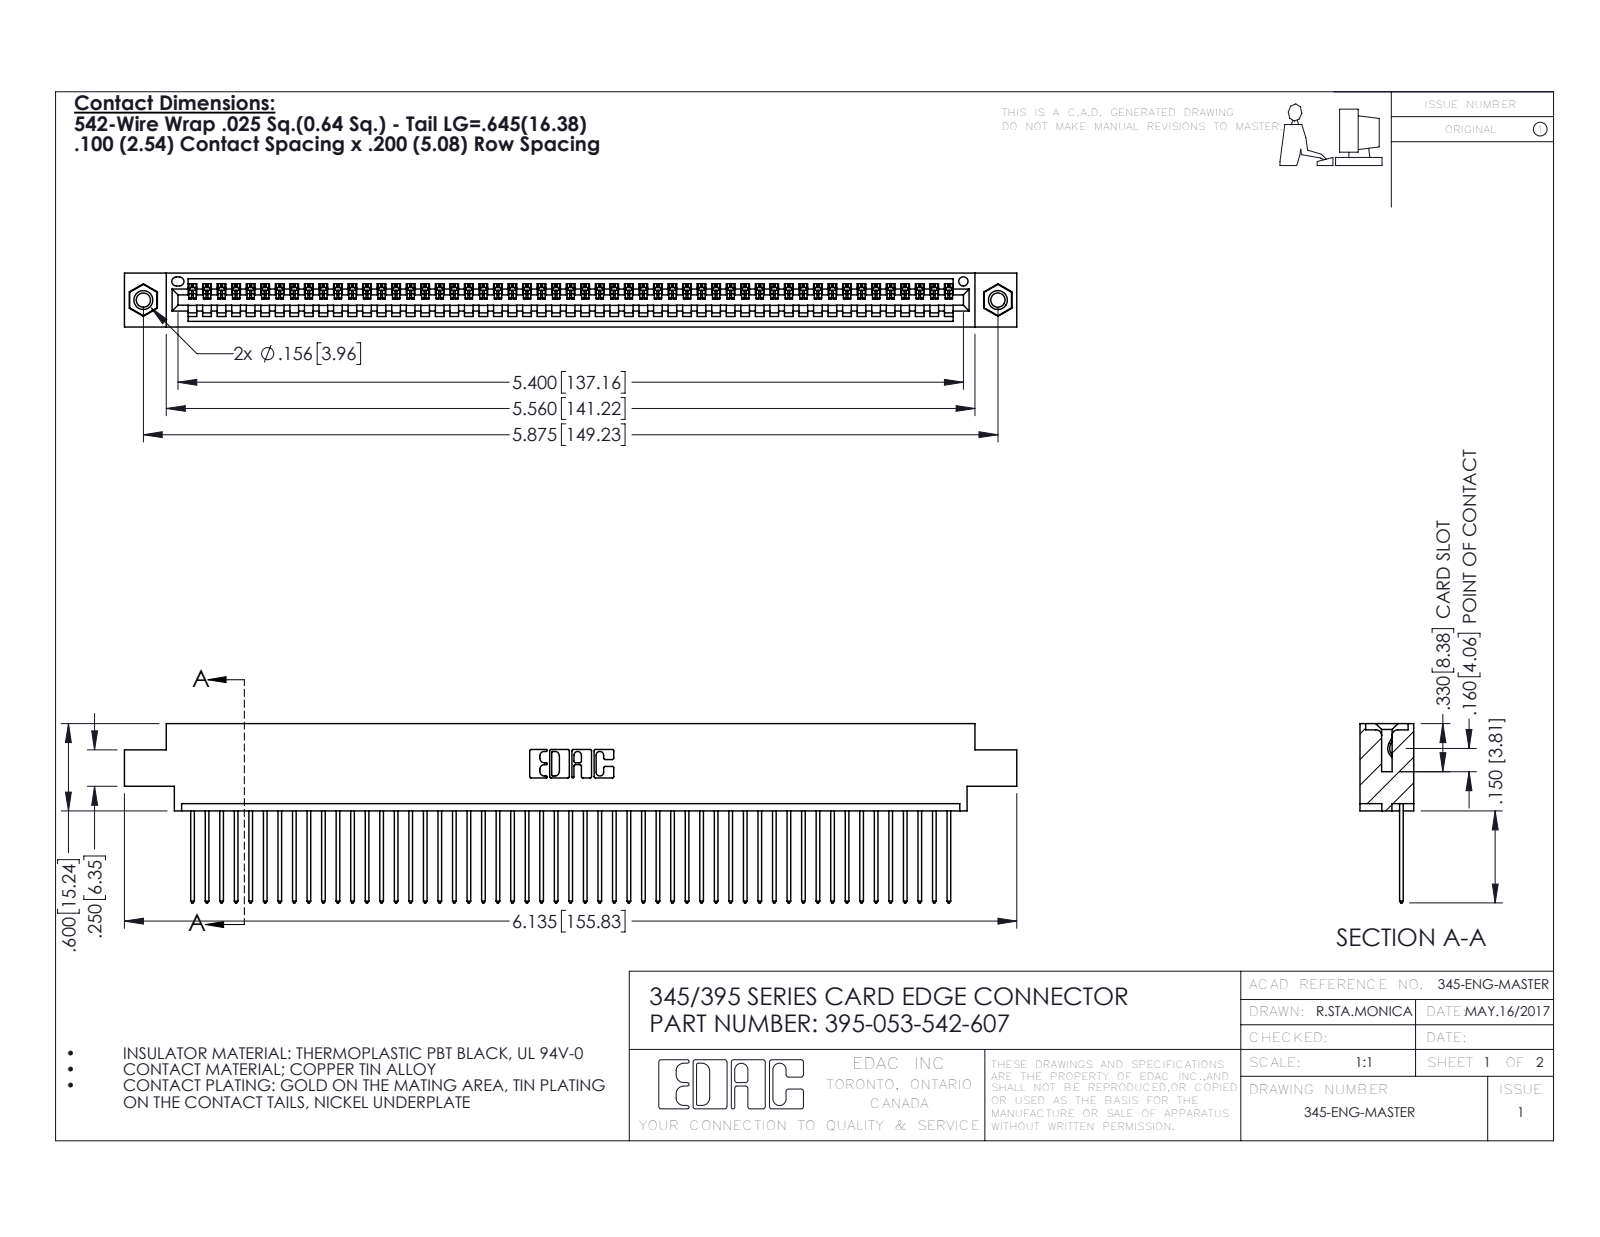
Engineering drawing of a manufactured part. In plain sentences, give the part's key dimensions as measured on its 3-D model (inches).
The part is named "395-053-542-607; 345 Part_0.170 Offset - 0.156 Dia-TI; 345-292-001_345-293-142; 345-250-001_345-250-005-103". Its 3-D file was written by "SolidWorks 2016 (CONFIG_CONTROL_DESIGN)". It is 56 solids with 3264 faces: 2236 planar, 1012 cylindrical and 16 other. Overall it measures 6.135 by 1.232 by 0.37 inches. Its volume is 0.908 cubic inches and its surface area 32.29 square inches. Round holes: 2 of diameter 0.098, 2 of diameter 0.125, 2 of diameter 0.156, 1 of diameter 0.064. Round bosses or shafts: 2 of diameter 0.155. Partial cylindrical surfaces (rounded edges, fillets, slot ends): 106 of radius 0.006, 106 of radius 0.01, 22 of radius 0.01, 6 of radius 0.007, 6 of radius 0.031, 3 of radius 0.026, 2 of radius 0.031, 2 of radius 0.04. The main face-to-face distances are 0.072, 0.298, 0.37, 0.098, 0.272, 0.025, 0.2, 0.225, 0.175, 0.149. The hole center spacings are 0.27, 5.639, 5.875.
